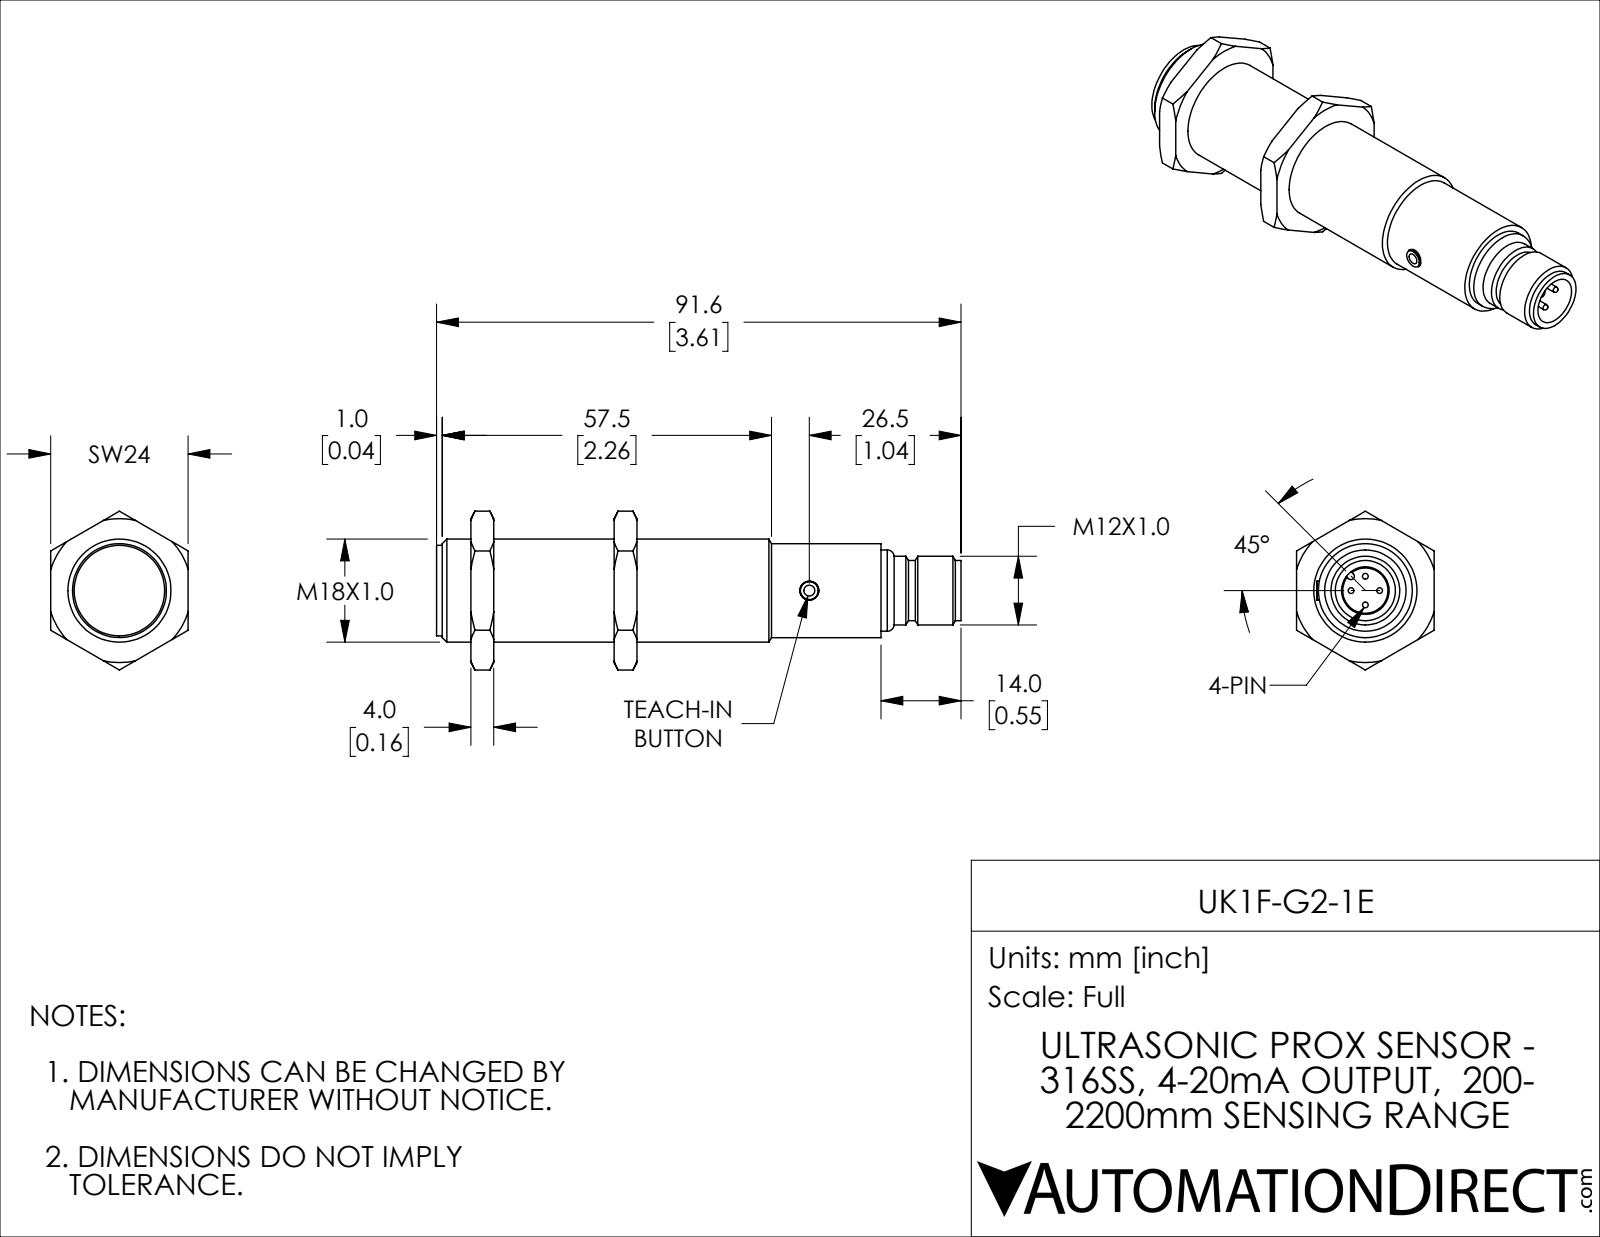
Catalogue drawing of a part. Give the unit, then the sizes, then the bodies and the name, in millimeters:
Units: millimetres
Overall size (bounding box): 91.6 × 27.7 × 24
Round holes (diameter × count): ⌀3.3 ×1, ⌀8.3 ×1, ⌀18 ×1
Round bosses / shafts (diameter × count): ⌀1 ×4, ⌀16.4 ×1, ⌀15.8 ×1, ⌀14.2 ×1, ⌀12 ×1, ⌀10.5 ×1
Partial cylindrical surfaces — rounded edges, fillets, slot ends (radius × count): R0.6 ×1
Main face-to-face distances: 25, 4, 24, 29, 21, 6, 10, 31, 35, 77.6
Volume: 21 930 mm³ · Surface area: 7 723 mm²
Bodies: 4 solids, 113 faces (27 planar, 35 cylindrical, 51 other)
Part name (STEP PRODUCT): UK1F-G2-1E
STEP written by: SolidWorks 2018 (AUTOMOTIVE_DESIGN)
